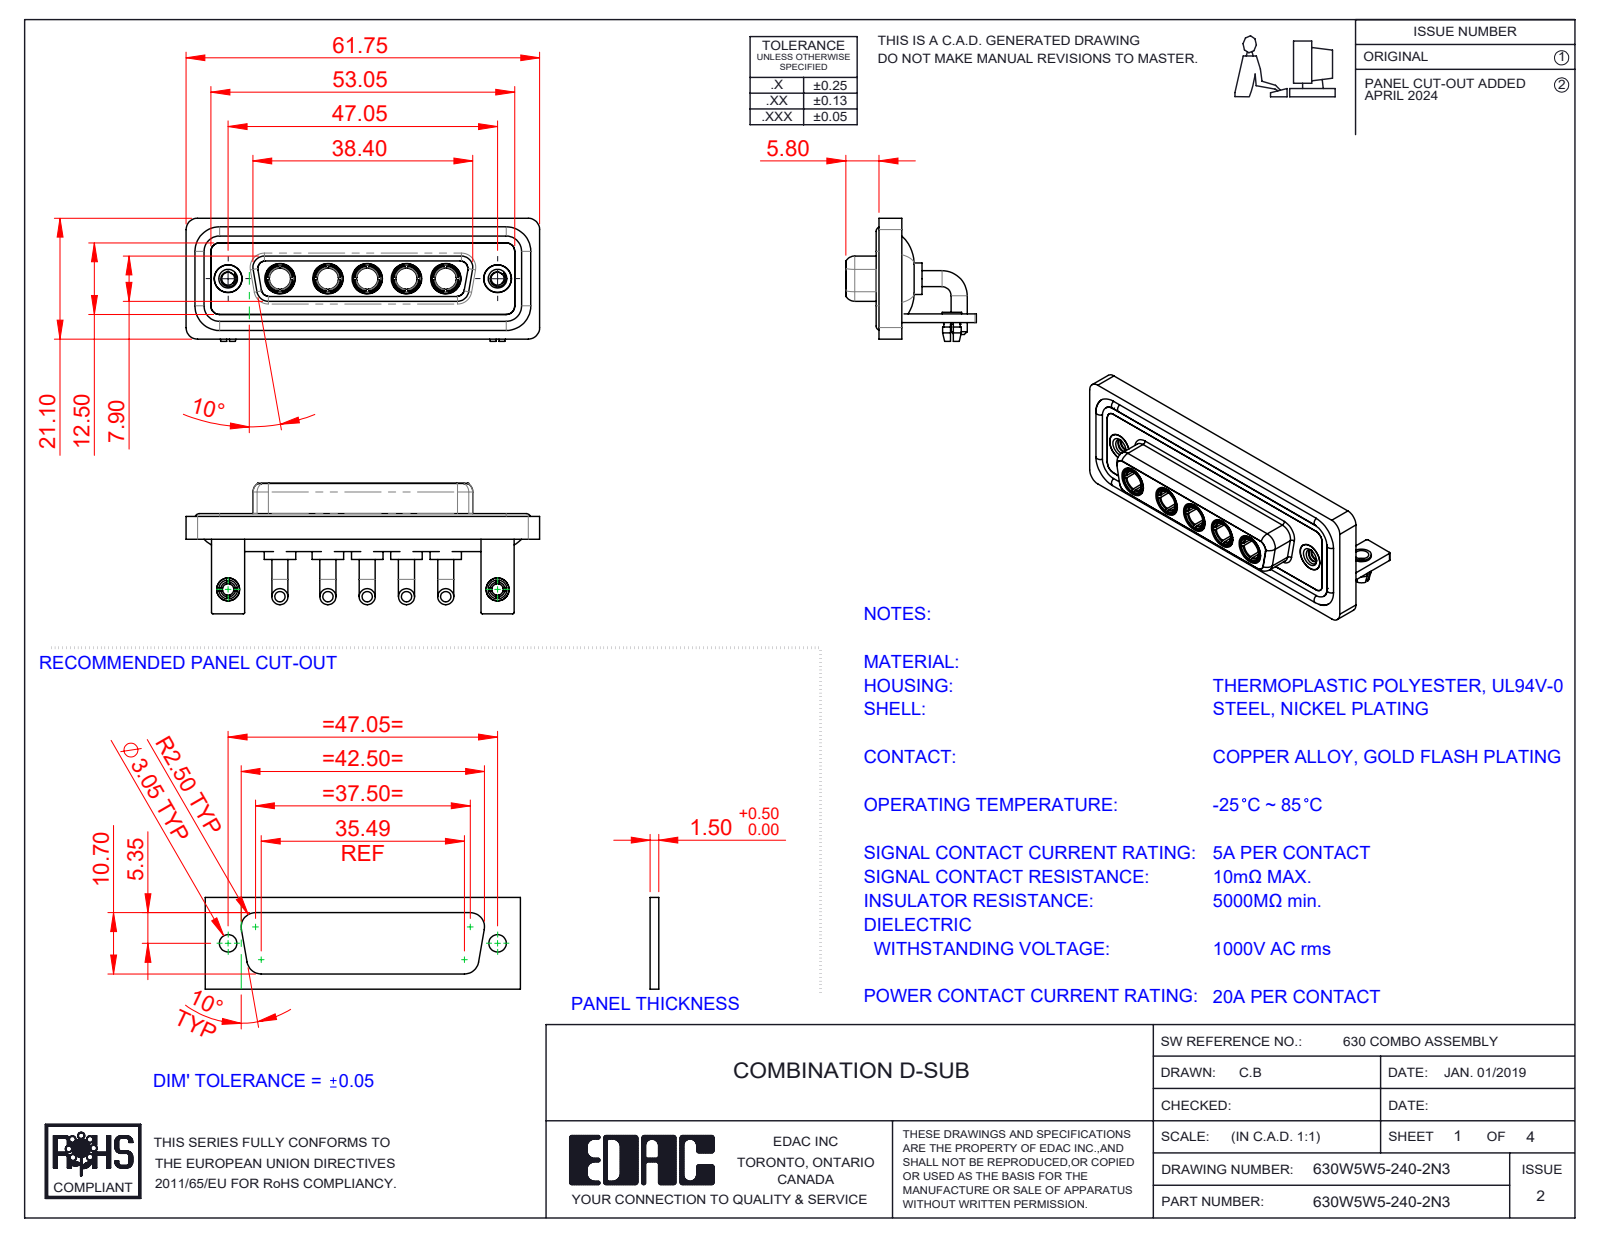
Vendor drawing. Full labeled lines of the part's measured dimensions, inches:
Part name (STEP PRODUCT): 630Combo Housing_5W5; 630Combo Shell Front_25 Contacts; 630Combo Waterproof Housing_25 Contacts; 630W5W5-240-2N3 (+5 more)
STEP written by: SolidWorks 2023 (CONFIG_CONTROL_DESIGN)
Units: inches
Bodies: 21 solids, 916 faces (318 planar, 369 cylindrical, 229 other)
Overall size (bounding box): 2.431 × 0.898 × 0.846
Volume: 0.539 in³ · Surface area: 22.88 in²
Round holes (diameter × count): ⌀0.191 ×7, ⌀0.146 ×5, ⌀0.209 ×5, ⌀0.079 ×2, ⌀0.089 ×2, ⌀0.098 ×2, ⌀0.126 ×2, ⌀0.157 ×2, ⌀0.159 ×2, ⌀0.197 ×2
Round bosses / shafts (diameter × count): ⌀0.11 ×10, ⌀0.217 ×5, ⌀0.205 ×5, ⌀0.195 ×5, ⌀0.187 ×5, ⌀0.148 ×5, ⌀0.063 ×4, ⌀0.195 ×2
Partial cylindrical surfaces — rounded edges, fillets, slot ends (radius × count): R0.079 ×19, R0.059 ×18, R0.01 ×16, R0.053 ×8, R0.063 ×8, R0.02 ×5, R0.083 ×5, R0.024 ×4
Main face-to-face distances: 0.016, 0.071, 0.114, 0.059, 0.146, 0.161, 0.043, 0.055, 0.063, 0.098
Hole centre spacings: 0.27, 0.356, 1.496, 1.852, 0.27, 0.33, 0.54, 0.541
